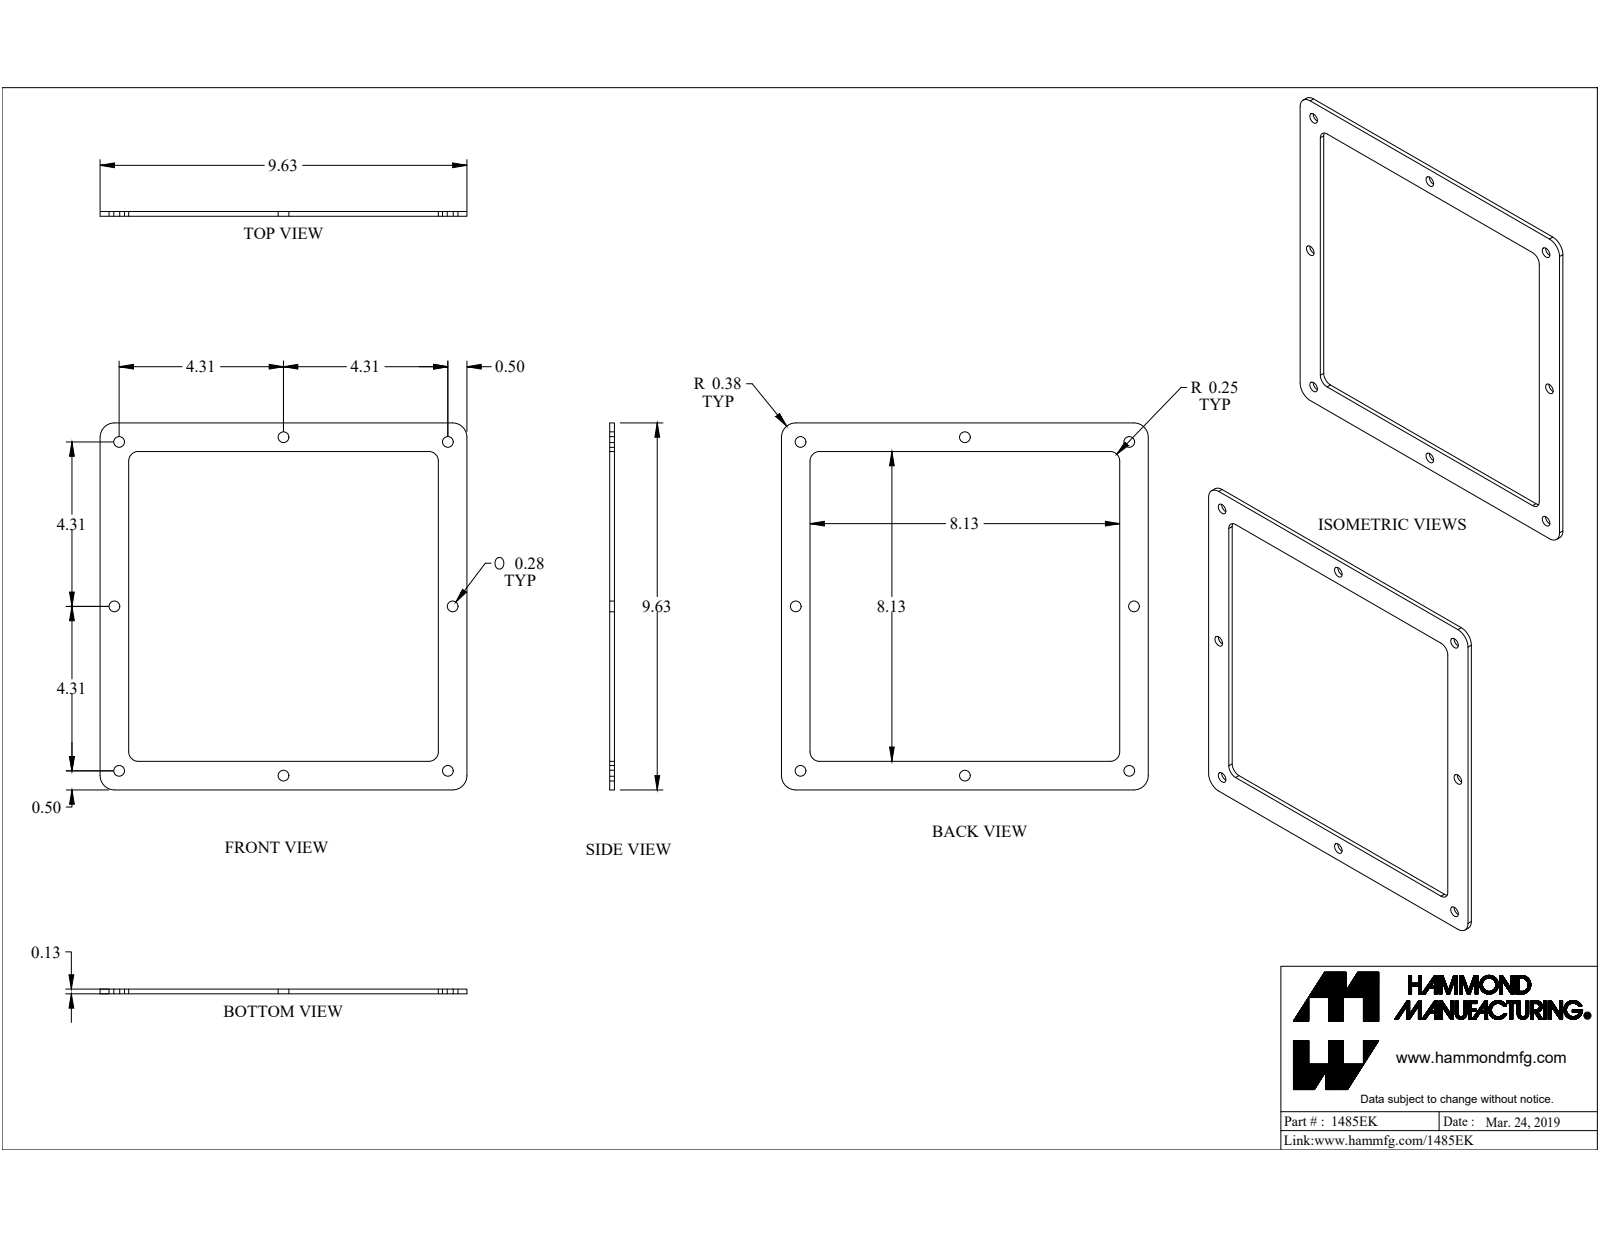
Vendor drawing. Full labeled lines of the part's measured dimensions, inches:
Part name (STEP PRODUCT): 1485EK
STEP written by: SolidWorks 2019 (CONFIG_CONTROL_DESIGN)
Units: inches
Bodies: 1 solid, 26 faces (10 planar, 16 cylindrical, 0 other)
Overall size (bounding box): 9.625 × 9.625 × 0.125
Volume: 3.258 in³ · Surface area: 61.75 in²
Round holes (diameter × count): ⌀0.281 ×8
Partial cylindrical surfaces — rounded edges, fillets, slot ends (radius × count): R0.25 ×4, R0.375 ×4
Main face-to-face distances: 0.125, 0.75, 8.875, 9.625, 8.125
Hole centre spacings: 4.315, 9.755, 6.276, 8.625, 8.875, 12.198
